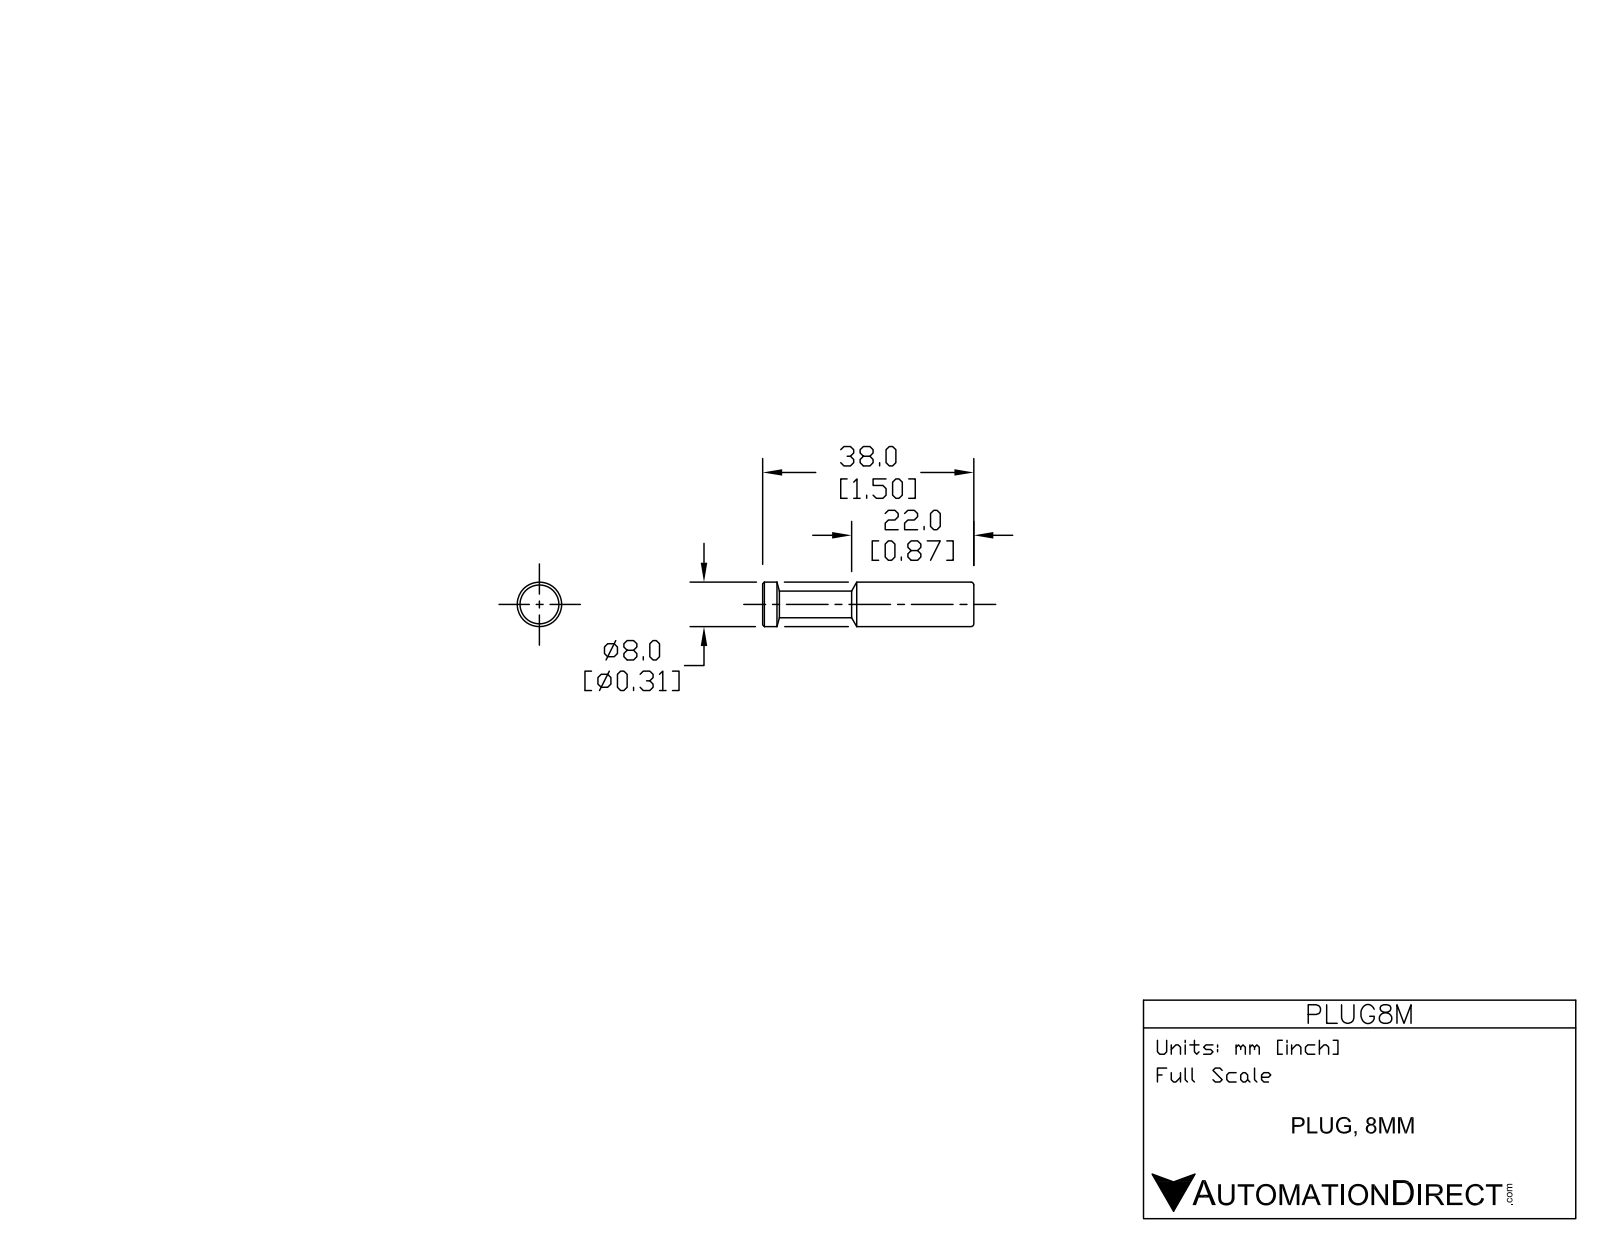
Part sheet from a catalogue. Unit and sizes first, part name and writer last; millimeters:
Units: millimetres
Overall size (bounding box): 38 × 8 × 8
Round bosses / shafts (diameter × count): ⌀8 ×1, ⌀4.8 ×1
Main face-to-face distances: 38
Volume: 1 500 mm³ · Surface area: 952 mm²
Bodies: 1 solid, 16 faces (2 planar, 6 cylindrical, 8 other)
Part name (STEP PRODUCT): PLUG8M
STEP written by: SolidWorks 2015 (AUTOMOTIVE_DESIGN)
